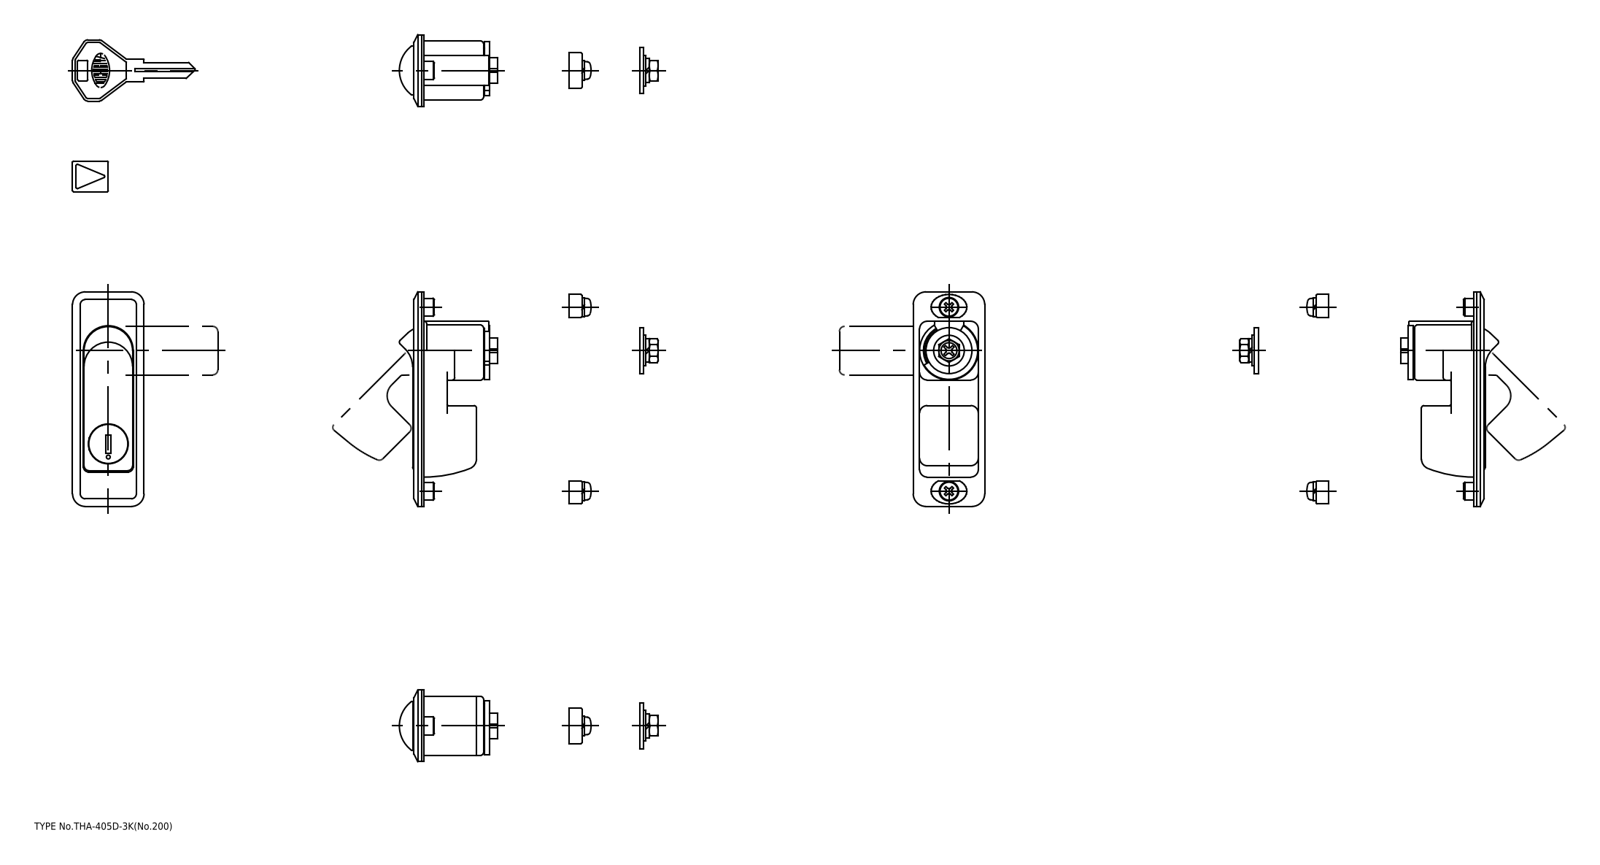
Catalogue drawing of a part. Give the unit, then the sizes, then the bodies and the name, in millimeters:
Units: millimetres
Overall size (bounding box): 102.48 × 84 × 28
Volume: 30 835 mm³ · Surface area: 26 280 mm²
Bodies: 13 solids, 446 faces (0 planar, 0 cylindrical, 446 other)
Part name (STEP PRODUCT): screw; bracket; washer; shaft (+8 more)
STEP written by: CADfix (AUTOMOTIVE_DESIGN)
